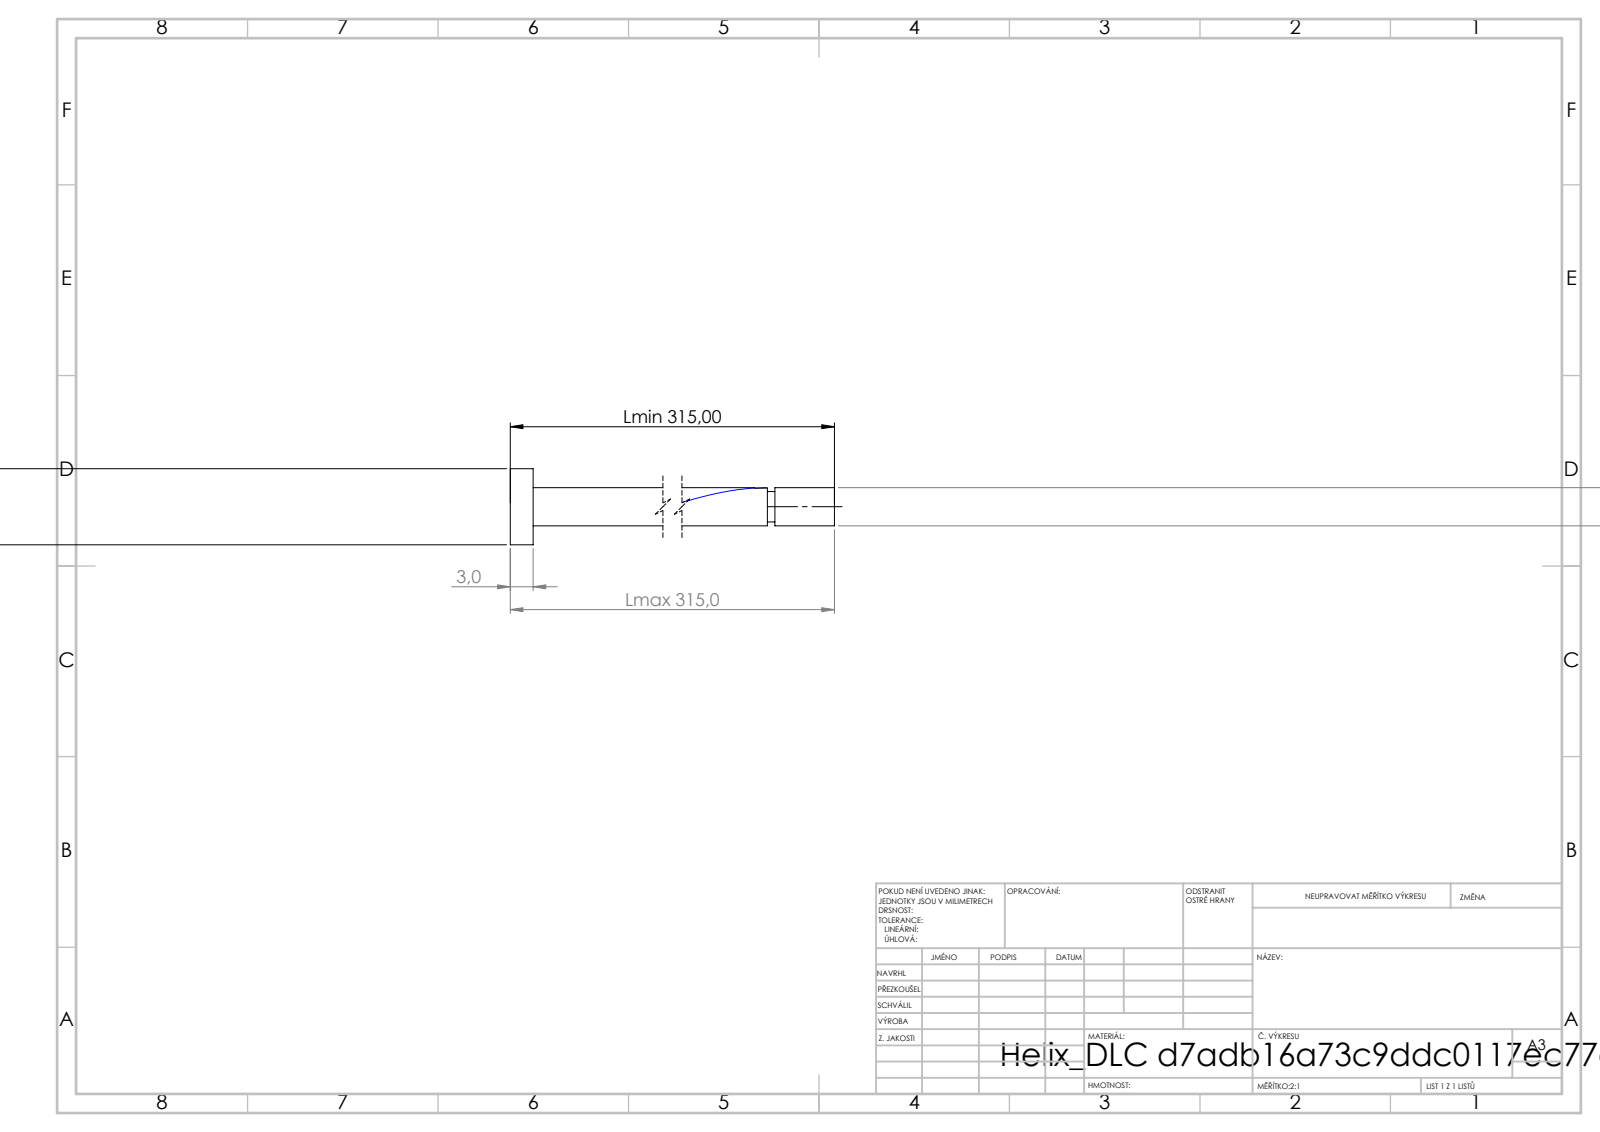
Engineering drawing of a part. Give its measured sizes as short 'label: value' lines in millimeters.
written by: SolidWorks 2019 (CONFIG_CONTROL_DESIGN)
unit: mm
bodies: 1 solid, 16 faces (6 planar, 9 cylindrical, 1 other)
size: 315 × 10 × 10
volume: 7 670 mm³; area: 6 891 mm²
bosses: 1× ⌀10, 1× ⌀5, 1× ⌀4
face distances: 3, 315, 312, 307.19, 304.19, 7.81, 306.19, 303.19, 1, 8.81
